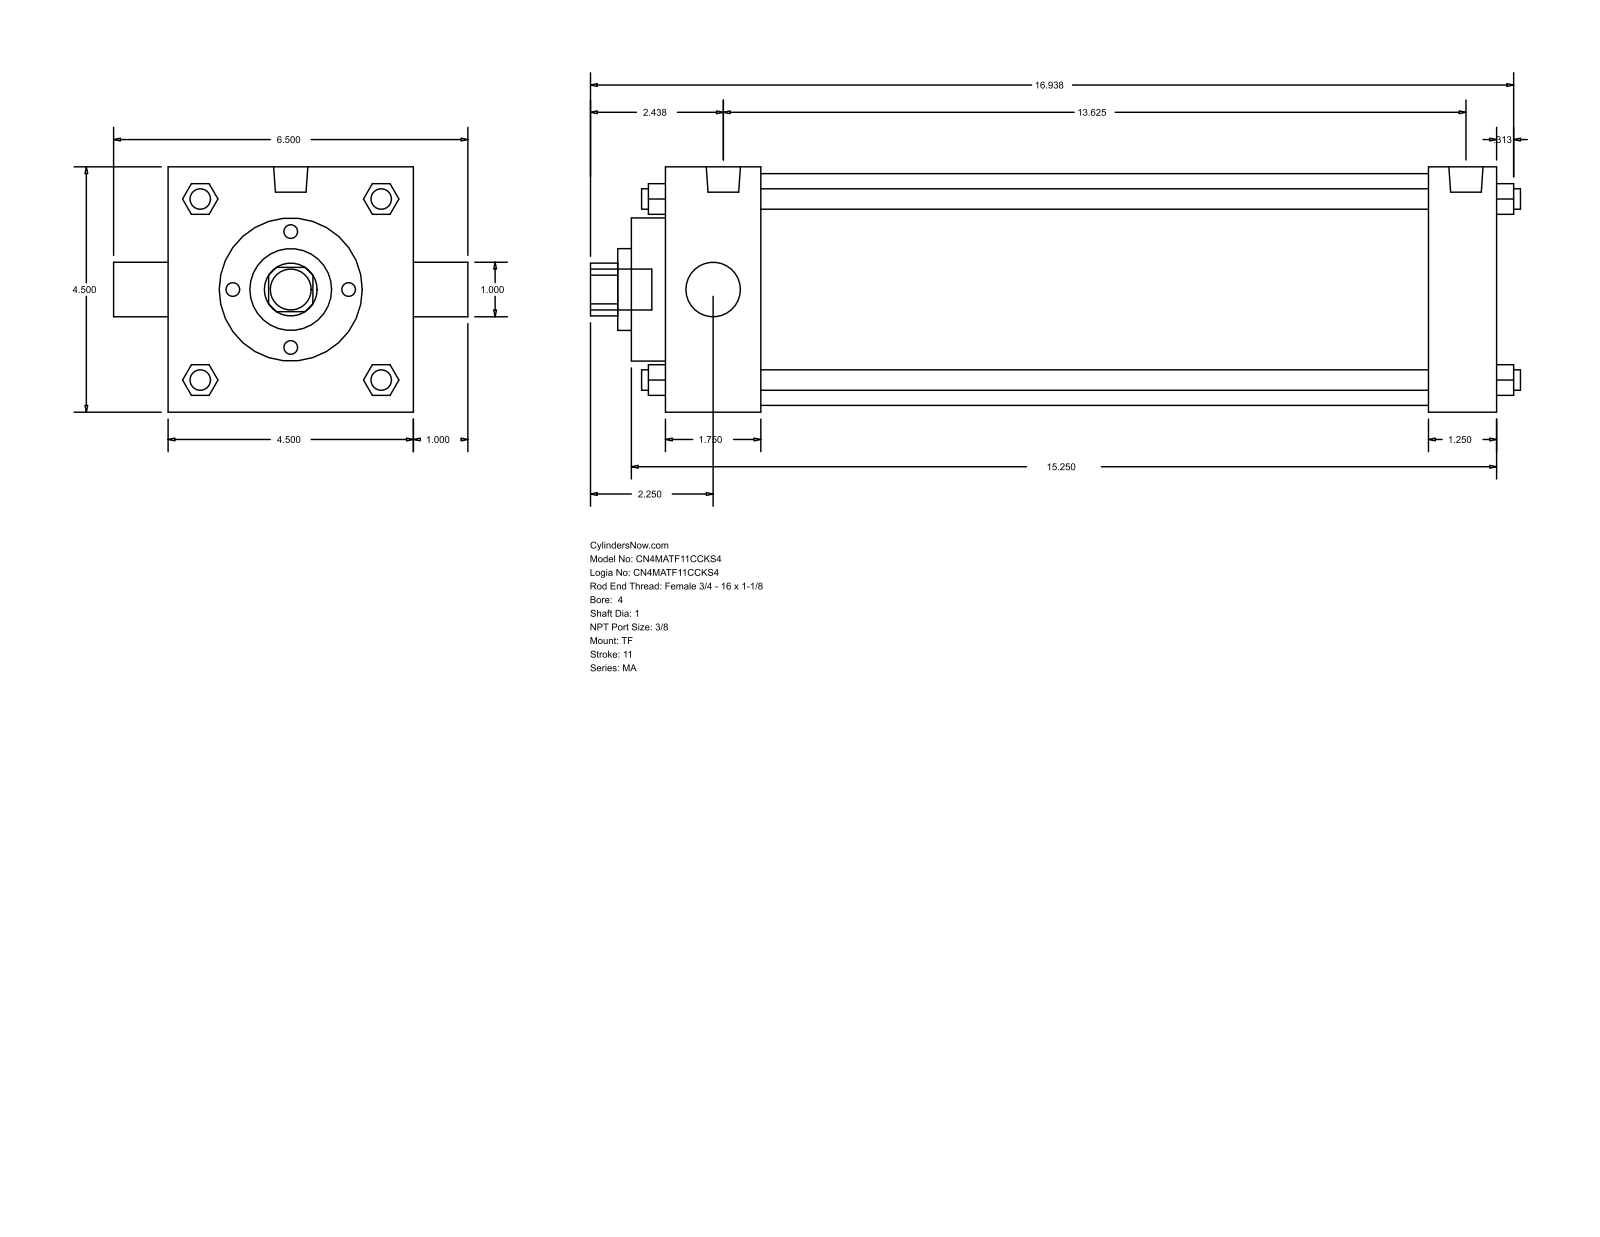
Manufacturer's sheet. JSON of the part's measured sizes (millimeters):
{"part_name": "MA_TF__0400_1", "step_written_by": "GSSL Pune (CONFIG_CONTROL_DESIGN)", "units": "millimeters", "bodies": {"solids": 0, "faces": 122, "planar": 93, "cylindrical": 29, "other": 0}, "overall_size": [433.39, 165.1, 114.3], "round_holes": [[25.4, 2], [38.1, 1], [66.67, 1], [107.95, 1]], "round_bosses_or_shafts": [[9.53, 4], [11.11, 3], [15.93, 2], [19.05, 1]], "partial_cylinders_radius": [[12.29, 1]], "face_to_face_distances": [114.3, 387.35, 355.6, 31.75, 44.46, 311.14, 342.89, 403.22, 15.87, 60.33]}
